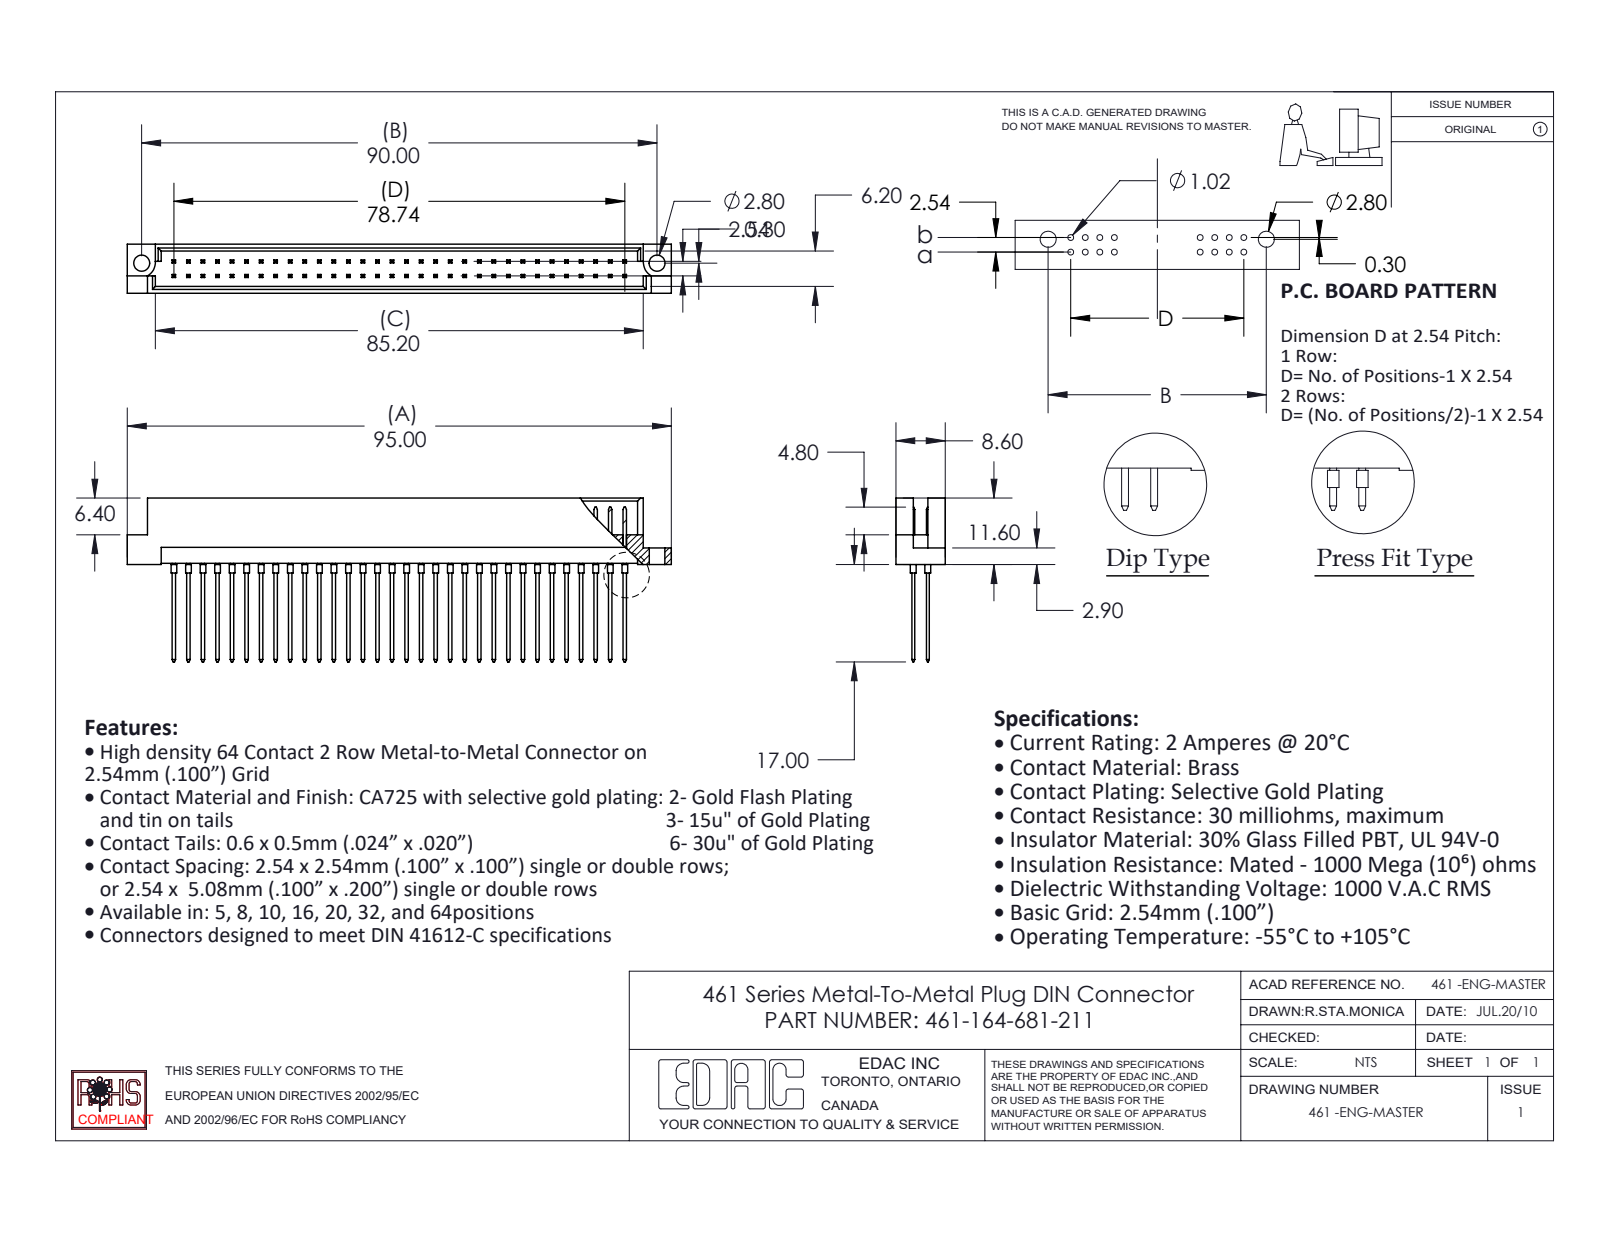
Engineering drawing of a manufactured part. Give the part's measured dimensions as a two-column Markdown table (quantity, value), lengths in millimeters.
| quantity | value |
| --- | --- |
| part name | 461 Part_64; 461-164-681-211; 461-290_81 |
| STEP written by | SolidWorks 2020 (CONFIG_CONTROL_DESIGN) |
| units | millimeters |
| bodies | 65 solids, 1713 faces (1578 planar, 135 cylindrical, 0 other) |
| overall size | 95 × 28.6 × 8.6 |
| volume | 5 214 mm³ |
| surface area | 9 601 mm² |
| round holes (diameter × count) | 2.8 × 2 |
| round bosses / shafts (diameter × count) | 1 × 64 |
| partial cylindrical surfaces (radius × count) | 2.8 × 2 |
| main face-to-face distances | 2.54, 1.2, 7.4, 3.28, 5.32, 2.08, 4.12, 2.78, 5.82, 1.58 |
| hole center spacings | 90 |
